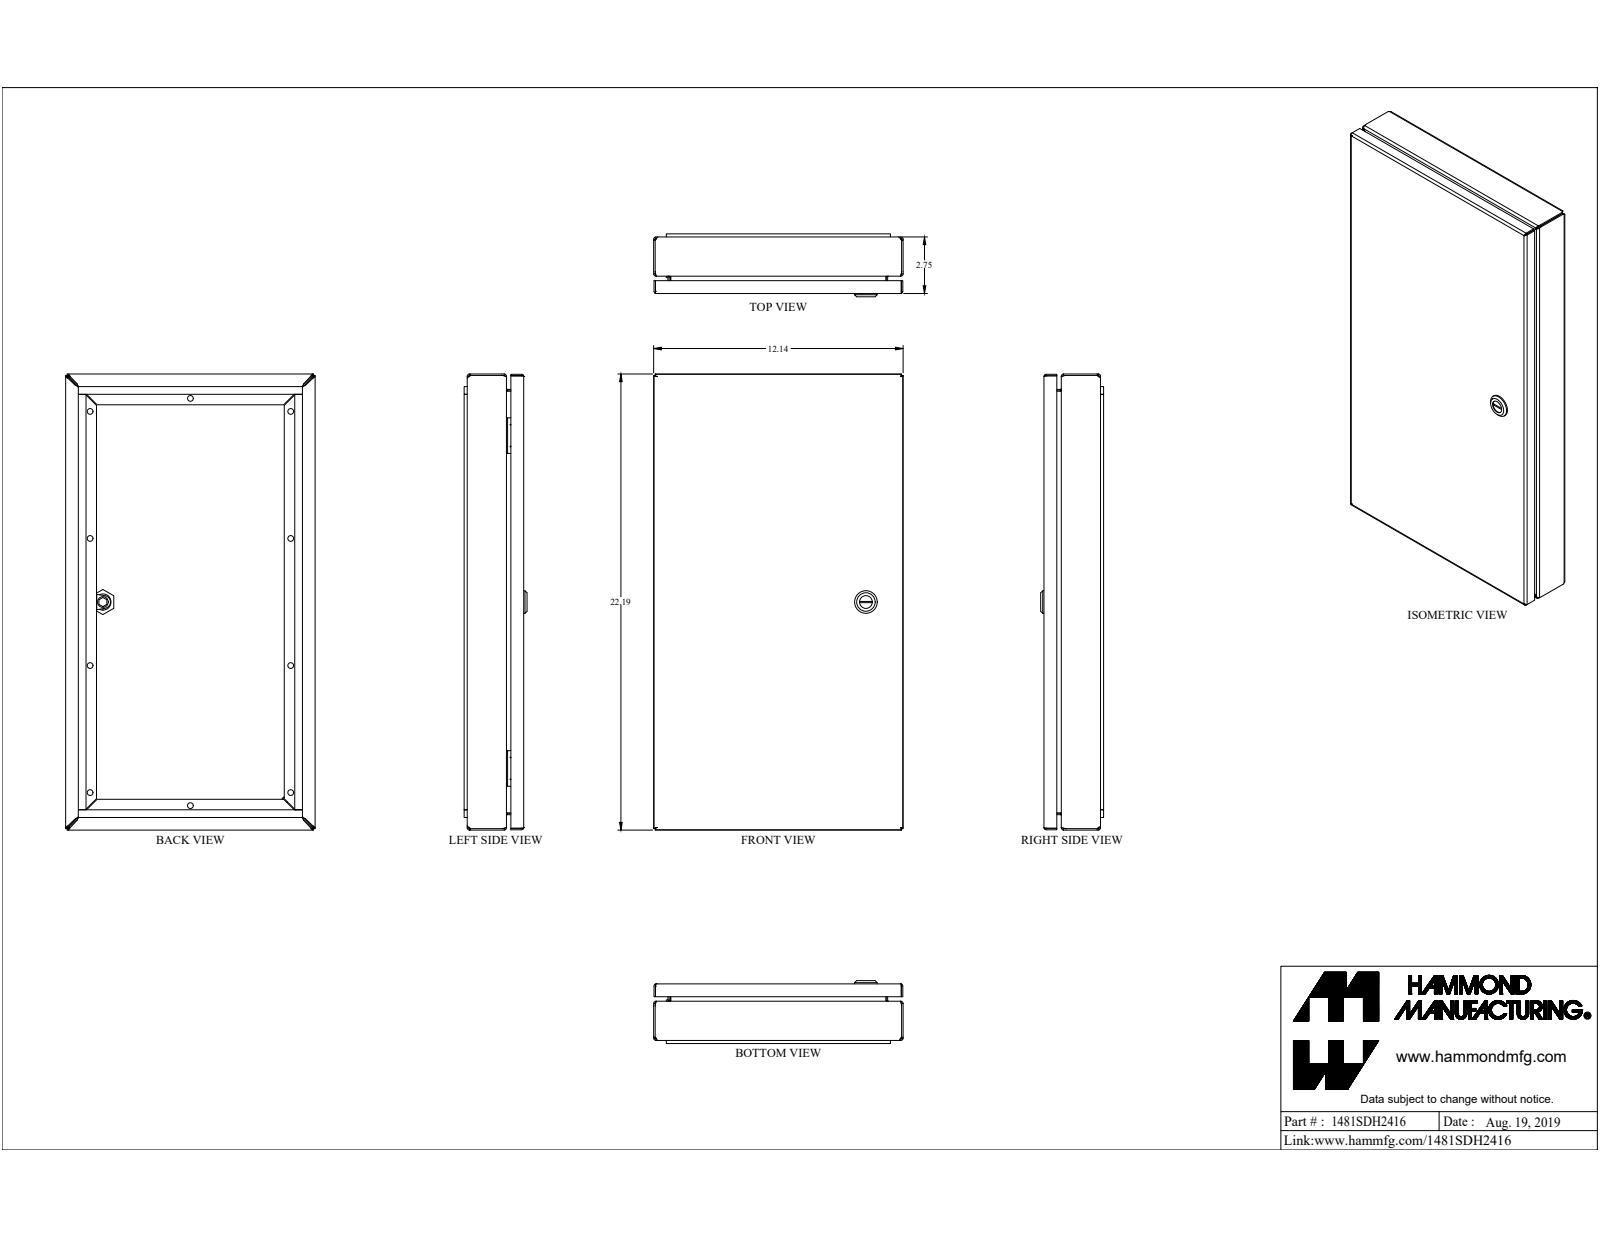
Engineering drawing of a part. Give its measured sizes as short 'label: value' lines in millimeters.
name: 1481SDH2416
written by: SolidWorks 2019 (CONFIG_CONTROL_DESIGN)
unit: mm
bodies: 23 solids, 616 faces (348 planar, 170 cylindrical, 98 other)
size: 563.6 × 308.4 × 77.7
volume: 935 000 mm³; area: 958 100 mm²
holes: 10× ⌀7.1, 1× ⌀4.4, 1× ⌀5.9, 1× ⌀6.1, 1× ⌀6.1, 1× ⌀15.9, 1× ⌀19.9
bosses: 1× ⌀27.9, 1× ⌀13.3, 1× ⌀11.6, 1× ⌀10.1, 1× ⌀9, 1× ⌀8, 1× ⌀7.4, 1× ⌀6.4
rounds: 28× R0.9, 28× R2.7, 12× R9.7, 8× R482.7, 4× R0.2, 4× R1.6, 4× R6.4, 4× R12.7
face distances: 1.8, 65.5, 21.4, 44.1, 306.5, 67.3, 63.7, 68, 46.6, 2.5
hole spacings: 293.5, 125, 157, 248, 400.2, 502.7, 80.1, 157
